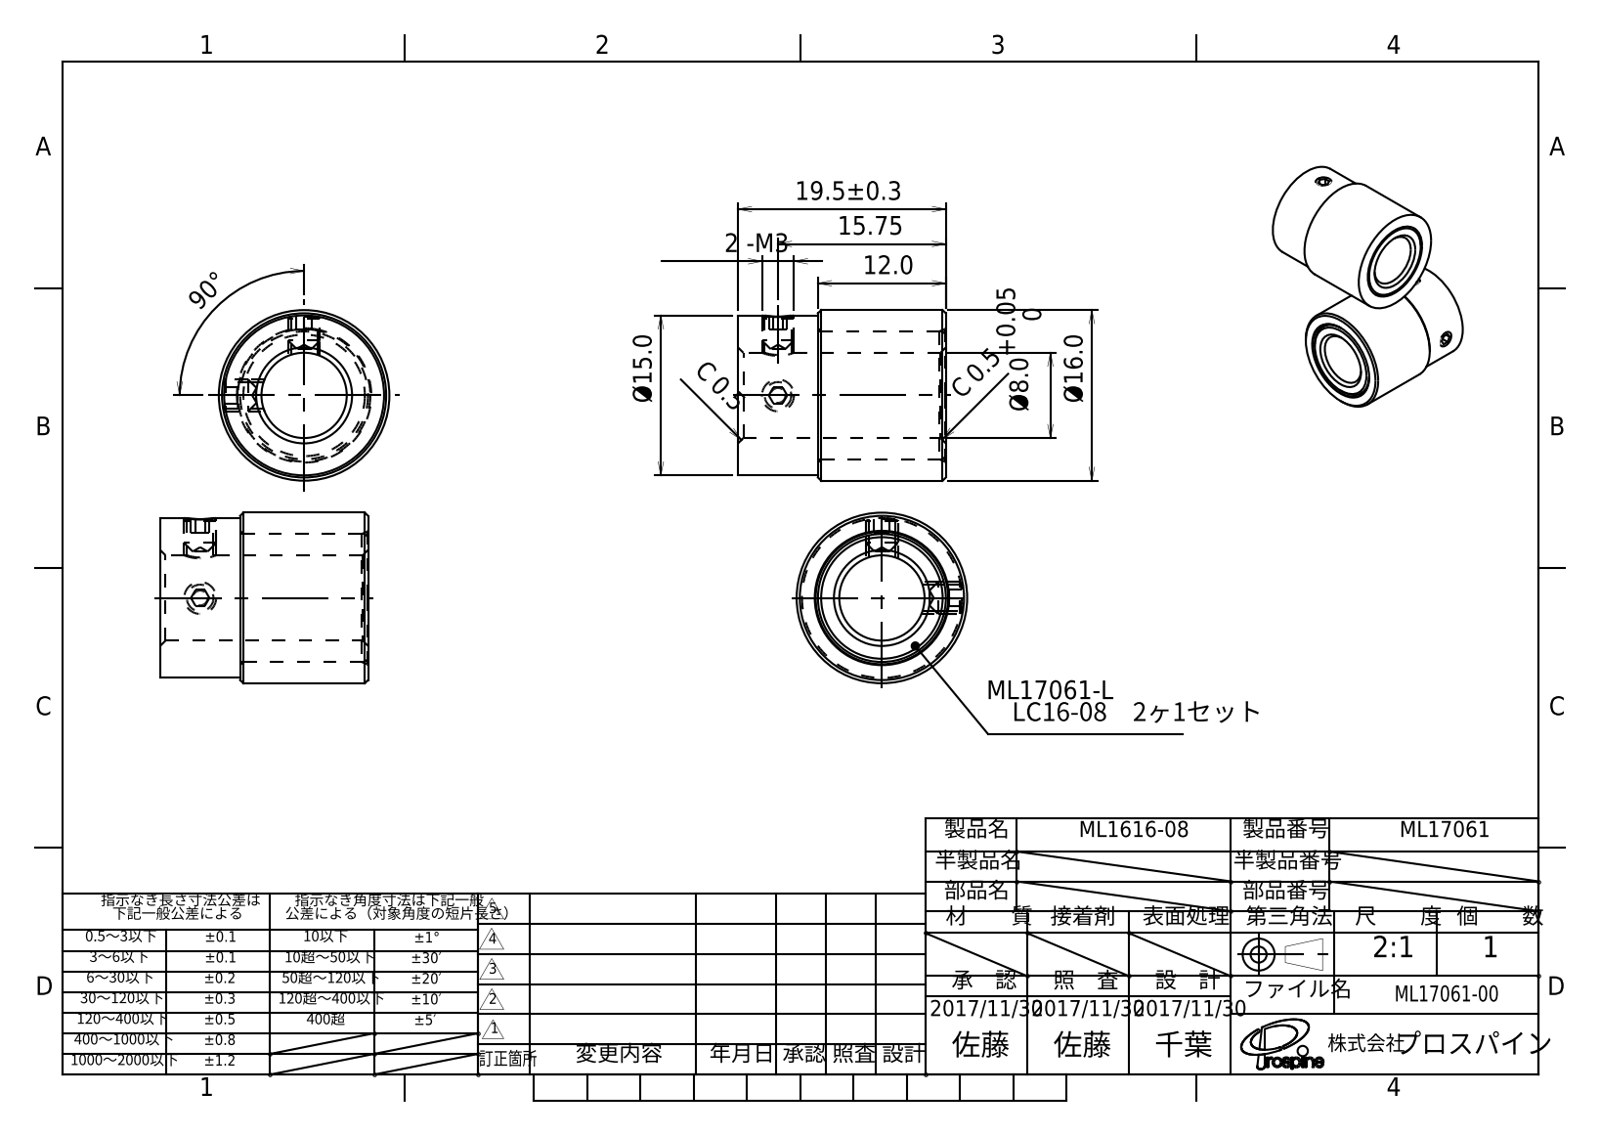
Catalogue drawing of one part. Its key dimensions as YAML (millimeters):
step_written_by: "PSStep 10.0 (CONFIG_CONTROL_DESIGN)"
units: millimeters
bodies: {solids: 10, faces: 112, planar: 58, cylindrical: 20, other: 34}
overall_size: [35, 21.5, 21.5]
volume: 5508
surface_area: 5782
round_holes:
  - {diameter: 2.5, count: 4}
  - {diameter: 8, count: 2}
  - {diameter: 12, count: 2}
round_bosses_or_shafts:
  - {diameter: 3, count: 4}
  - {diameter: 16, count: 2}
  - {diameter: 15, count: 2}
face_to_face_distances: [7.5, 19.5, 12, 1.5, 1.2, 1.46, 13.46, 19, 5.25, 6.75]
hole_center_spacings: [21.36, 13.79]
